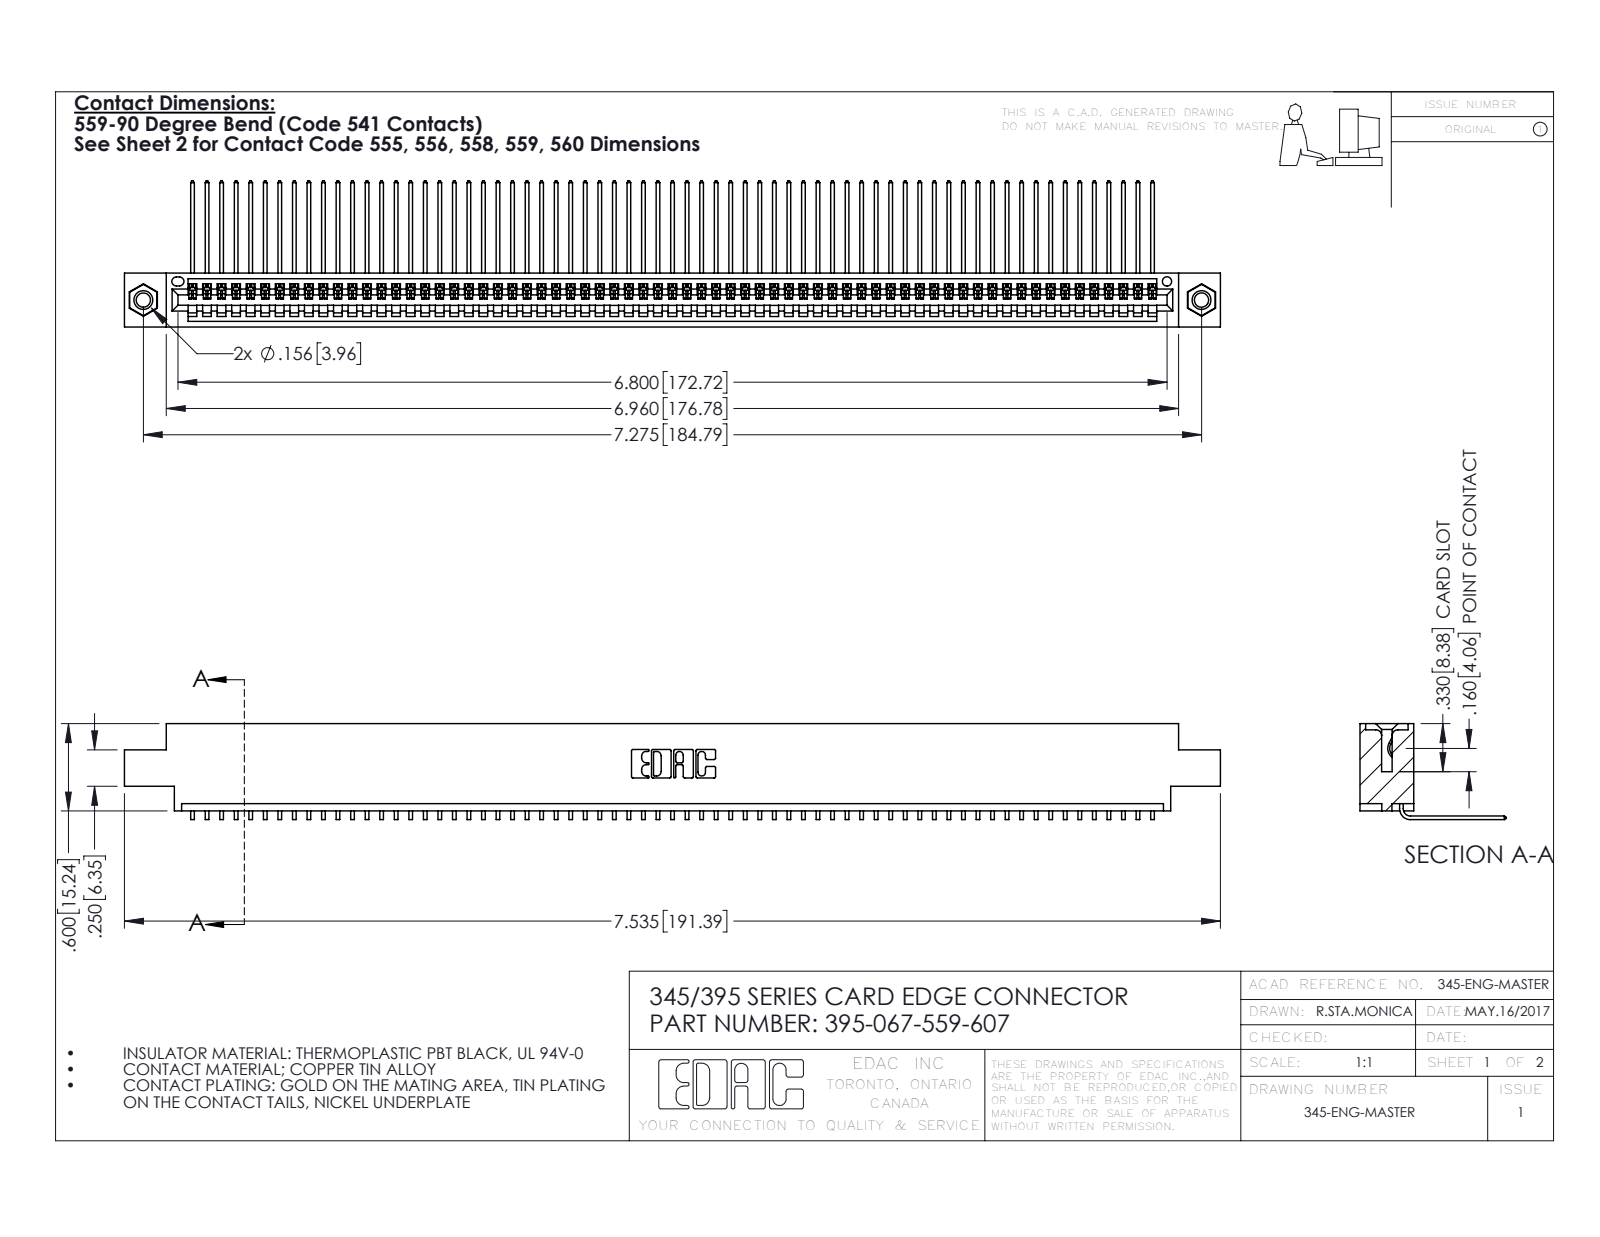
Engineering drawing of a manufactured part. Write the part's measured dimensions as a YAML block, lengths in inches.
part_name: "345-292-001_558 559 Tail - 1; 345 Part_0.170 Offset - 0.156 Dia-TI; 395-067-559-607; 345-250-001_345-250-005-103"
step_written_by: "SolidWorks 2016 (CONFIG_CONTROL_DESIGN)"
units: inches
bodies: {solids: 70, faces: 4210, planar: 2930, cylindrical: 1264, other: 16}
overall_size: [7.535, 1.005, 0.659]
volume: 1.128
surface_area: 40.87
round_holes:
  - {diameter: 0.098, count: 2}
  - {diameter: 0.125, count: 2}
  - {diameter: 0.156, count: 2}
  - {diameter: 0.064, count: 1}
round_bosses_or_shafts:
  - {diameter: 0.155, count: 2}
partial_cylinders:
  - {radius: 0.006, count: 134}
  - {radius: 0.01, count: 22}
  - {radius: 0.007, count: 6}
  - {radius: 0.031, count: 6}
  - {radius: 0.026, count: 3}
  - {radius: 0.031, count: 2}
  - {radius: 0.04, count: 2}
  - {radius: 0.014, count: 1}
face_to_face_distances: [0.072, 0.298, 0.37, 0.2, 0.098, 0.272, 0.025, 0.225, 0.175, 0.149]
hole_center_spacings: [0.27, 7.039, 7.275]
